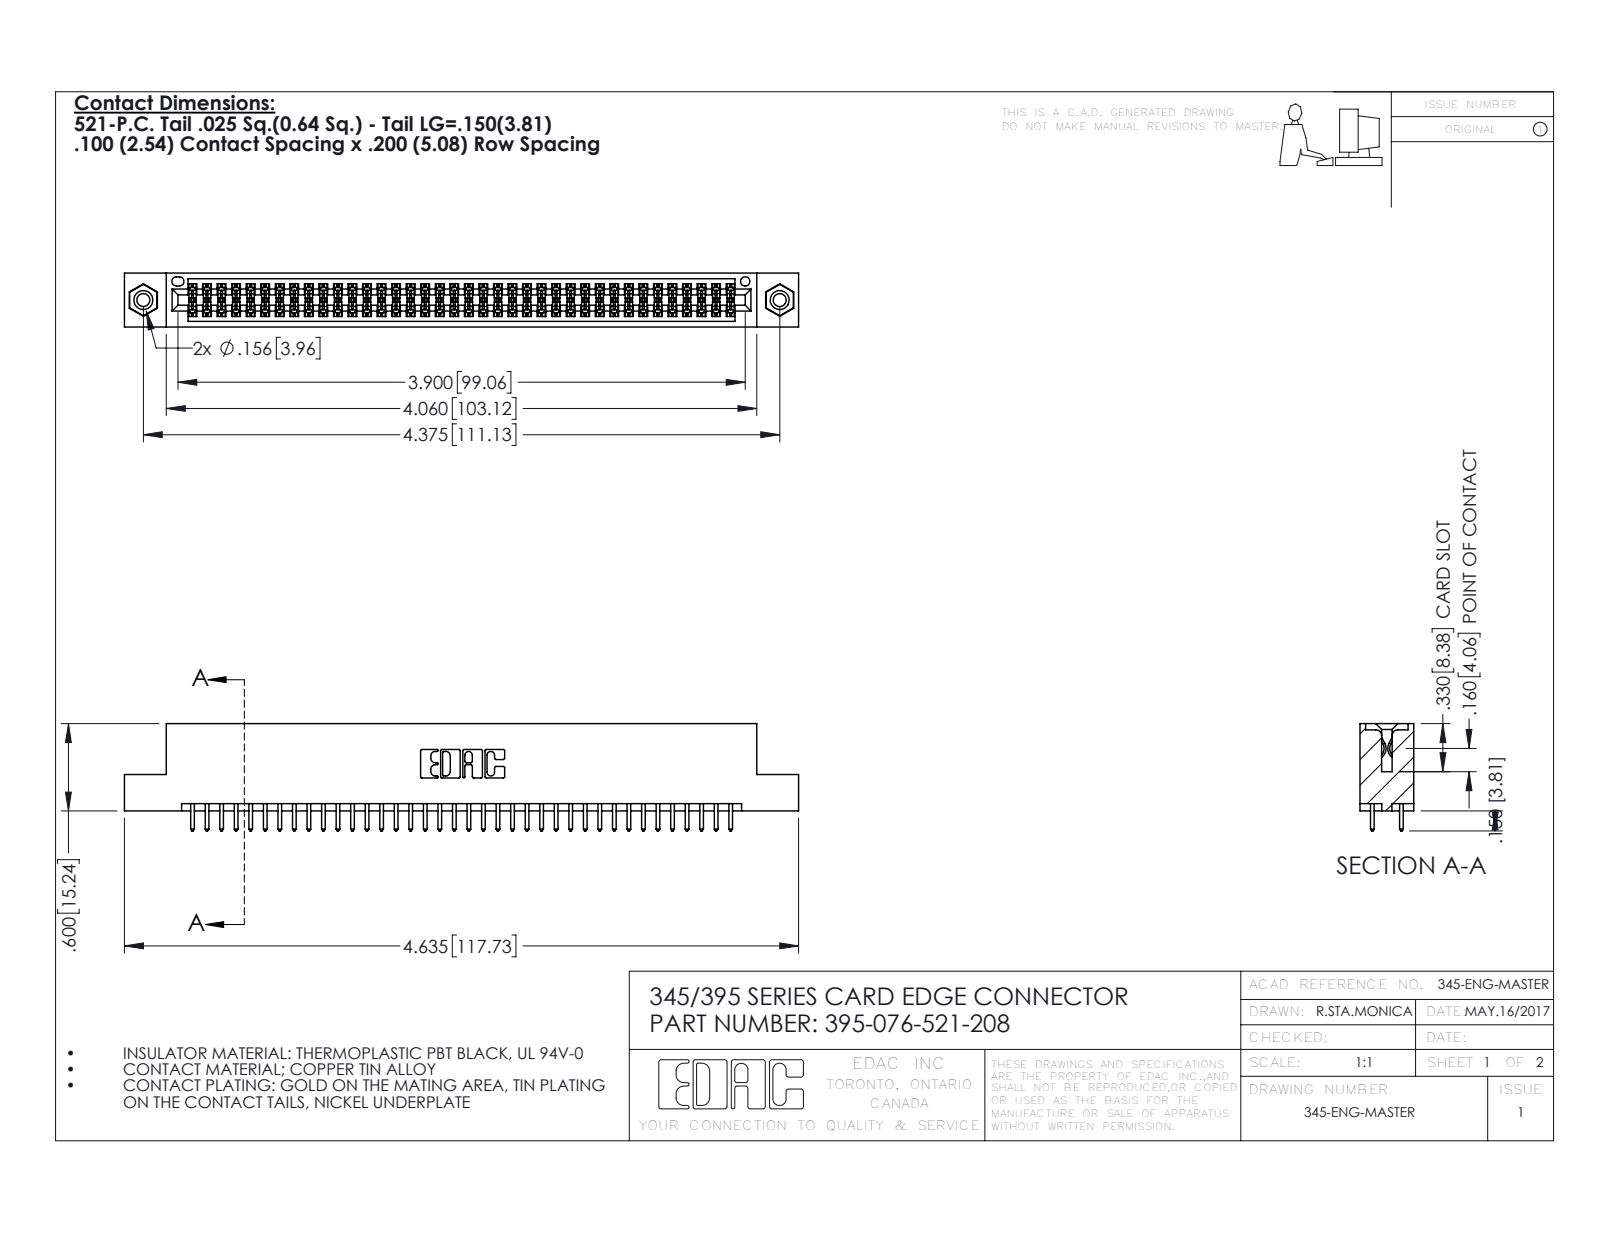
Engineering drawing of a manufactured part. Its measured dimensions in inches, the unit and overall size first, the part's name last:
Units: inches
Overall size (bounding box): 4.635 × 0.737 × 0.37
Round holes (diameter × count): ⌀0.089 ×2, ⌀0.125 ×2, ⌀0.156 ×2, ⌀0.064 ×1
Round bosses / shafts (diameter × count): ⌀0.155 ×2
Partial cylindrical surfaces — rounded edges, fillets, slot ends (radius × count): R0.006 ×114, R0.01 ×76, R0.01 ×22, R0.007 ×6, R0.031 ×6, R0.026 ×3, R0.014 ×2, R0.019 ×2
Main face-to-face distances: 0.072, 0.298, 0.2, 0.37, 0.098, 0.272, 0.025, 0.225, 0.175, 0.149
Hole centre spacings: 0.27, 4.139, 4.375
Volume: 0.693 in³ · Surface area: 25.62 in²
Bodies: 79 solids, 3986 faces (2620 planar, 1350 cylindrical, 16 other)
Part name (STEP PRODUCT): 345 Part_Flush Mounting Lugs - 0.156 Dia-TI; 395-076-521-208; 345-250-001_345-250-003-102; 345-292-001_345-293-121
STEP written by: SolidWorks 2016 (CONFIG_CONTROL_DESIGN)
